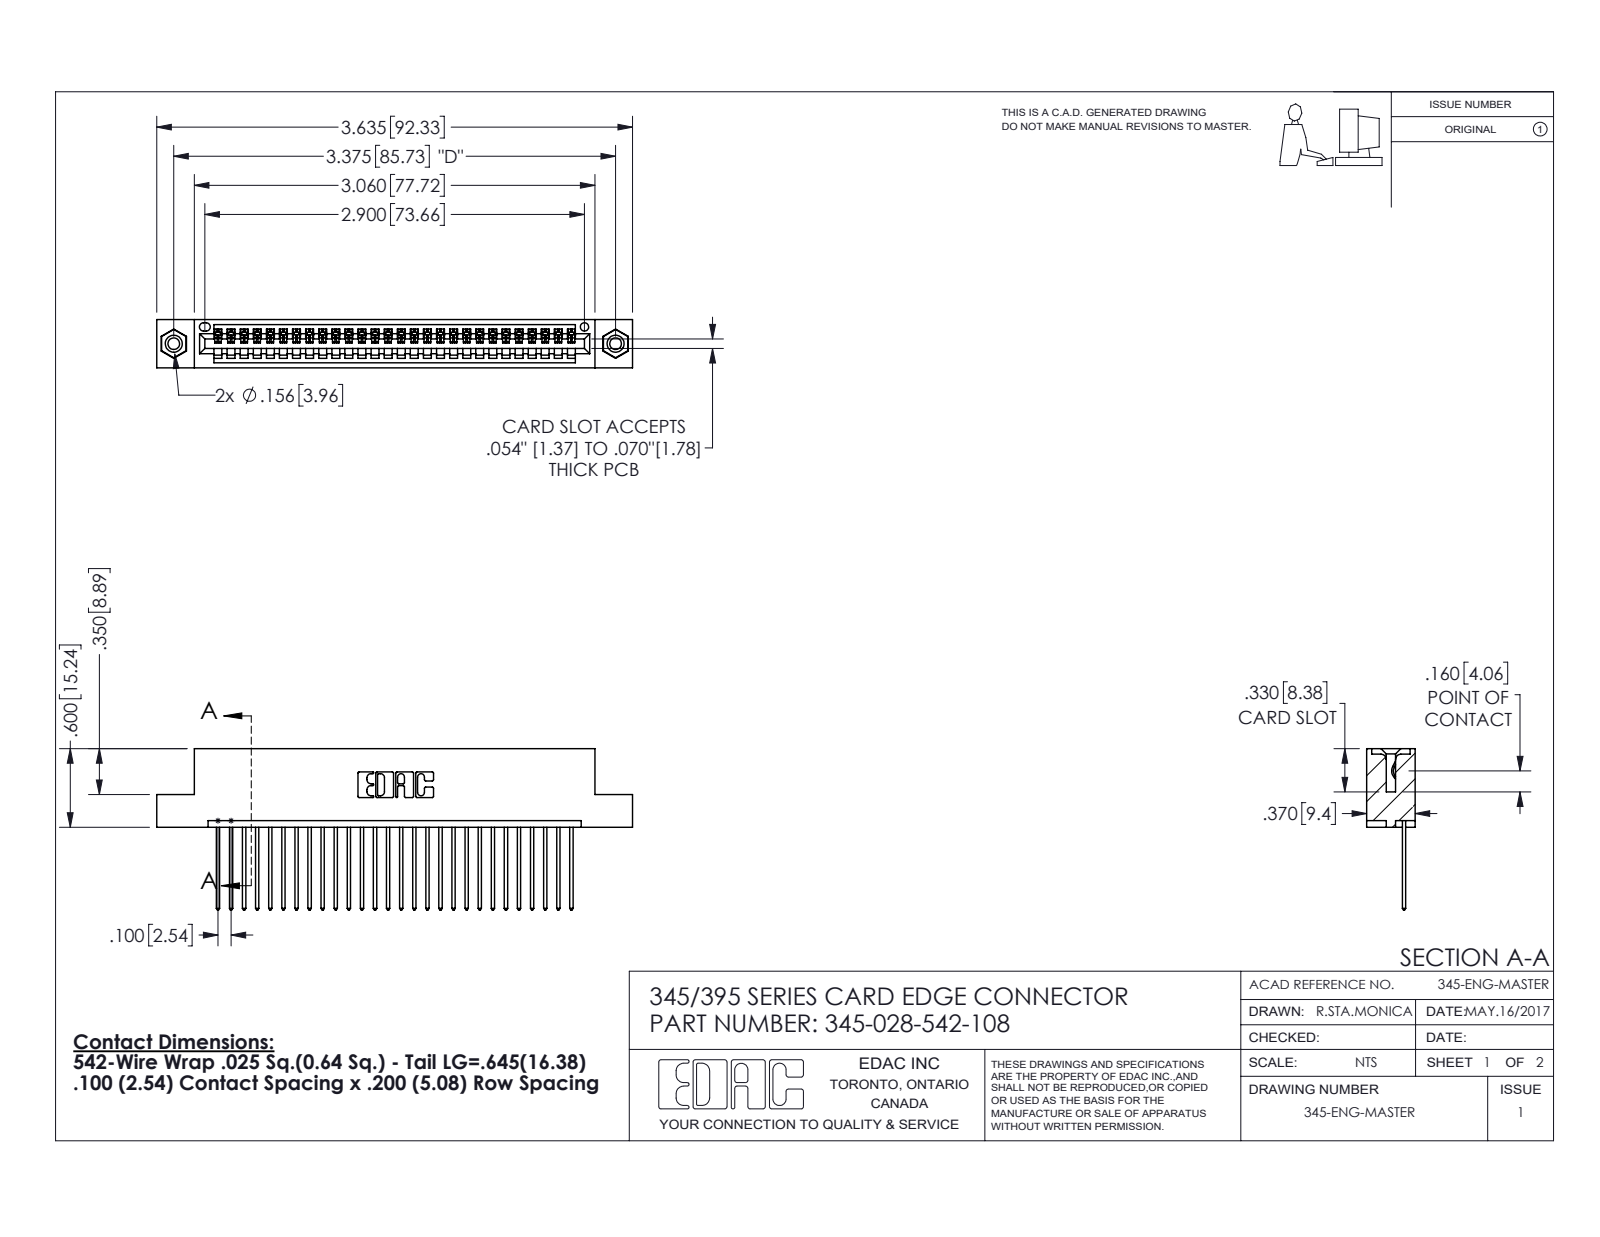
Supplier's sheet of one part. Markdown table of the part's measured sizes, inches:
| quantity | value |
| --- | --- |
| part name | 345 Part_Flush Mounting Lugs - 0.156 Dia-TI; 345-250-001_345-250-003-102; 345-028-542-108; 345-292-001_345-293-142 |
| STEP written by | SolidWorks 2016 (CONFIG_CONTROL_DESIGN) |
| units | inches |
| bodies | 31 solids, 1810 faces (1232 planar, 562 cylindrical, 16 other) |
| overall size | 3.635 × 1.232 × 0.37 |
| volume | 0.532 in³ |
| surface area | 18.29 in² |
| round holes (diameter × count) | 0.089 × 2, 0.125 × 2, 0.156 × 2, 0.064 × 1 |
| round bosses / shafts (diameter × count) | 0.155 × 2 |
| partial cylindrical surfaces (radius × count) | 0.006 × 56, 0.01 × 56, 0.01 × 22, 0.007 × 6, 0.031 × 6, 0.026 × 3, 0.031 × 2, 0.04 × 2 |
| main face-to-face distances | 0.072, 0.298, 0.2, 0.37, 0.098, 0.272, 0.025, 0.225, 0.149, 0.072 |
| hole center spacings | 0.27, 3.14, 3.375 |
